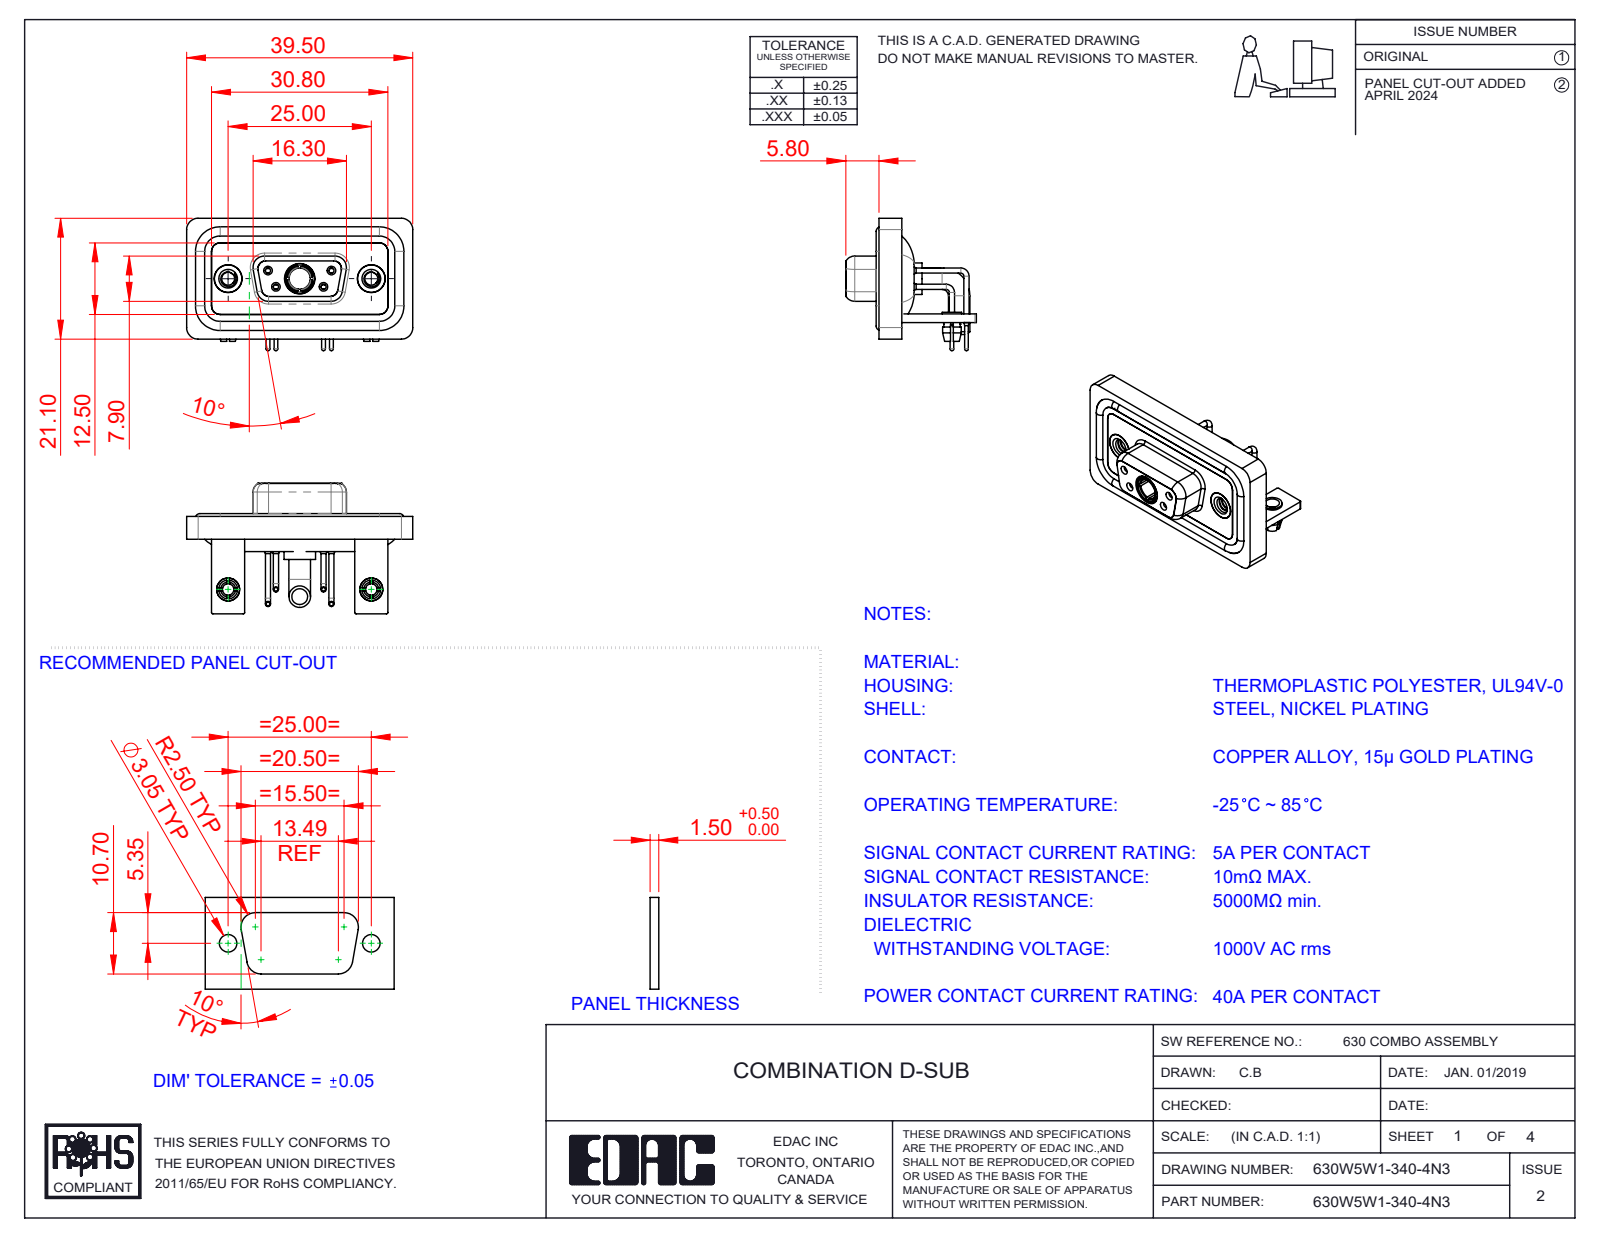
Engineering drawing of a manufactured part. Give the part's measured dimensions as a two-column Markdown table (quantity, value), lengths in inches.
| quantity | value |
| --- | --- |
| part name | 630W5W1-340-4N3; 630Combo Board Lock_50 Contacts; 630Combo Shell Rear_09 Contacts; 630Combo Threaded Rivet_2 (+7 more) |
| STEP written by | SolidWorks 2023 (CONFIG_CONTROL_DESIGN) |
| units | inches |
| bodies | 17 solids, 816 faces (262 planar, 361 cylindrical, 193 other) |
| overall size | 1.555 × 0.91 × 0.898 |
| volume | 0.324 in³ |
| surface area | 13.69 in² |
| round holes (diameter × count) | 0.079 × 6, 0.035 × 4, 0.043 × 4, 0.059 × 4, 0.191 × 3, 0.063 × 2, 0.067 × 2, 0.089 × 2, 0.098 × 2, 0.126 × 2, 0.157 × 2, 0.159 × 2 |
| round bosses / shafts (diameter × count) | 0.063 × 6, 0.035 × 4, 0.026 × 4, 0.195 × 2, 0.189 × 2, 0.157 × 2, 0.148 × 2, 0.134 × 2 |
| partial cylindrical surfaces (radius × count) | 0.079 × 19, 0.059 × 18, 0.01 × 16, 0.053 × 8, 0.063 × 8, 0.02 × 5, 0.024 × 4, 0.026 × 4 |
| main face-to-face distances | 0.016, 0.114, 0.059, 0.071, 0.043, 0.146, 0.063, 0.031, 0.098, 0.122 |
| hole center spacings | 0.124, 0.225, 0.28, 0.492, 0.713, 0.984, 0.173, 0.173 |
